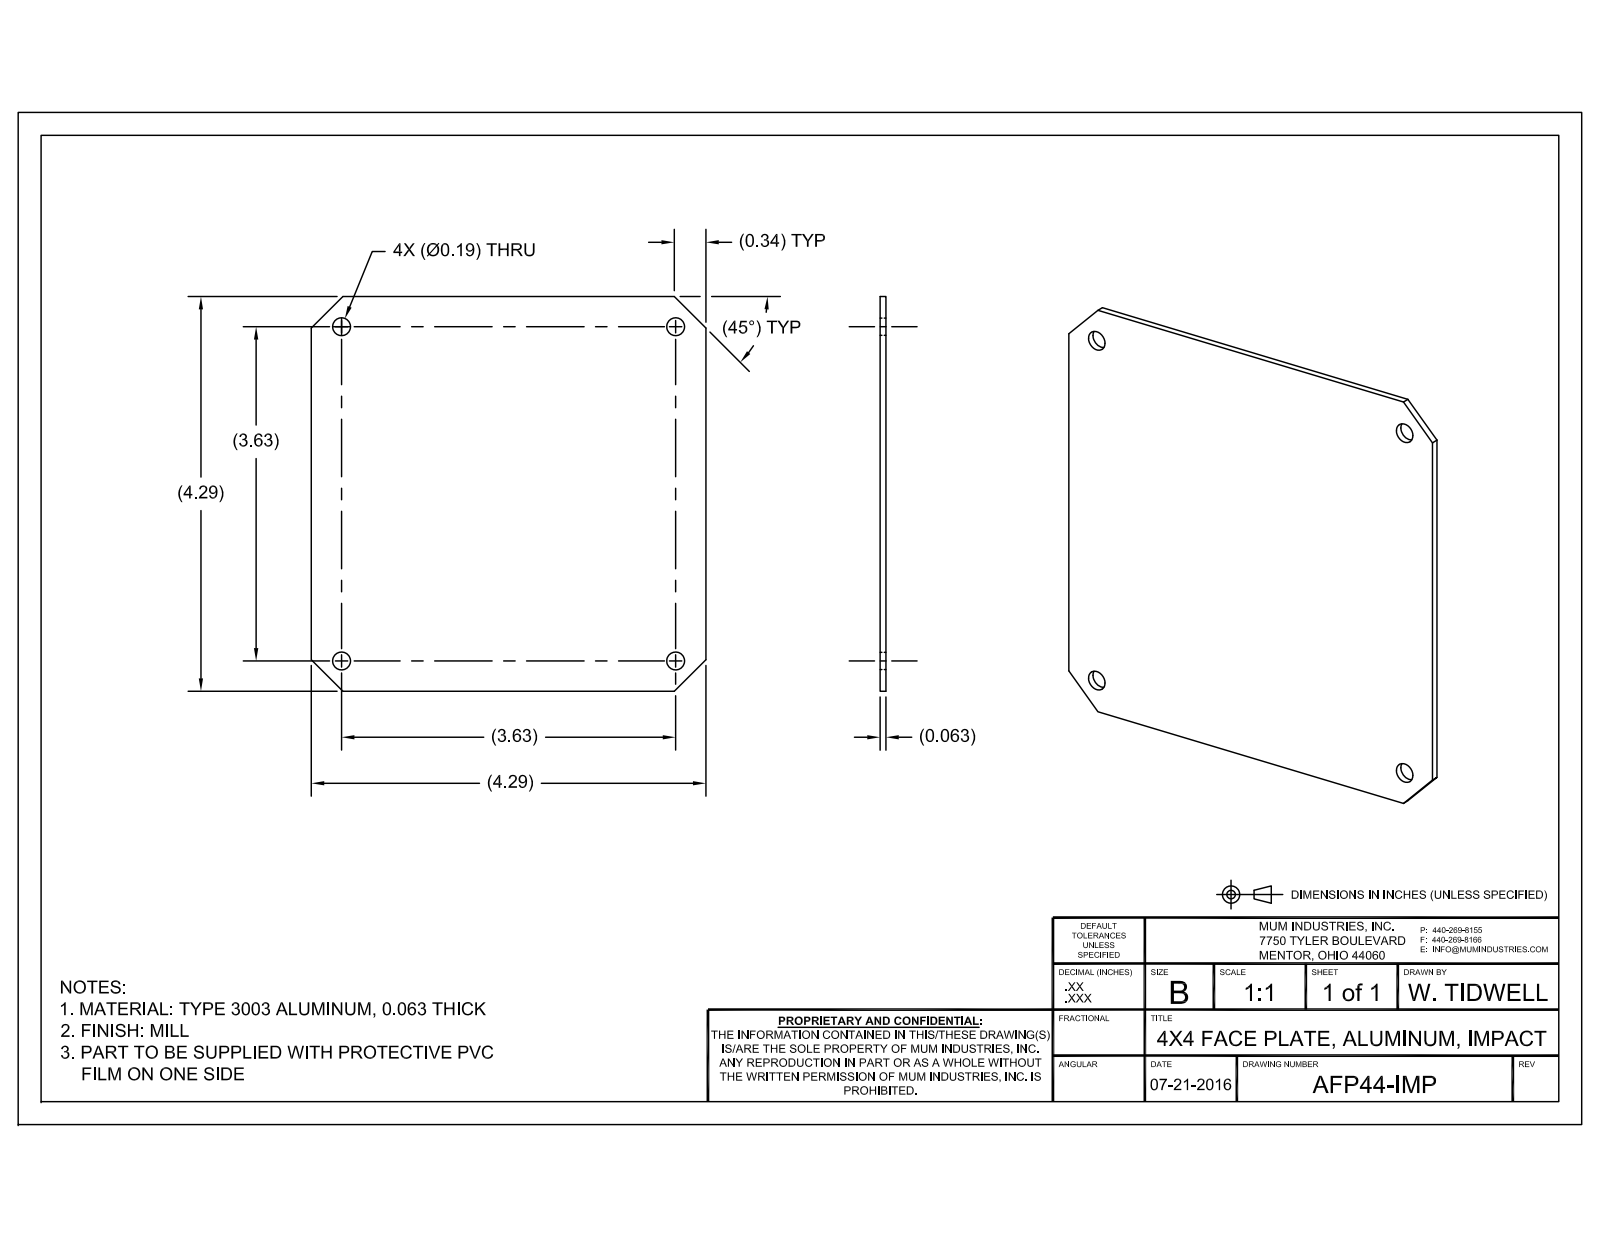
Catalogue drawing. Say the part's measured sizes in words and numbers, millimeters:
The part is named "AFP44-IMP; SUPPORT-FP-4043; 9912597-82-10; AFPK44-IMP_ASM". Its 3-D file was written by "CREO PARAMETRIC BY PTC INC, 2016050 (CONFIG_CONTROL_DESIGN)". It is 13 solids with 1578 faces: 362 planar, 636 cylindrical and 580 other. Overall it measures 110.5 by 110.5 by 62.4 millimeters. Its volume is 48 340 cubic millimeters and its surface area 49 060 square millimeters. Round holes: 4 of diameter 4.9. Round bosses or shafts: 8 of diameter 8.2, 8 of diameter 4.2, 8 of diameter 3. Partial cylindrical surfaces (rounded edges, fillets, slot ends): 100 of radius 0.3, 60 of radius 0.8, 36 of radius 0.9, 20 of radius 1.2, 16 of radius 2.3, 16 of radius 3.3, 12 of radius 1.5, 8 of radius 0.3. The main face-to-face distances are 1.6, 2.6, 48.8, 47.2, 66.5, 61.4, 5.1, 2.8, 50, 51.6. The hole center spacings are 92.3, 130.5.
